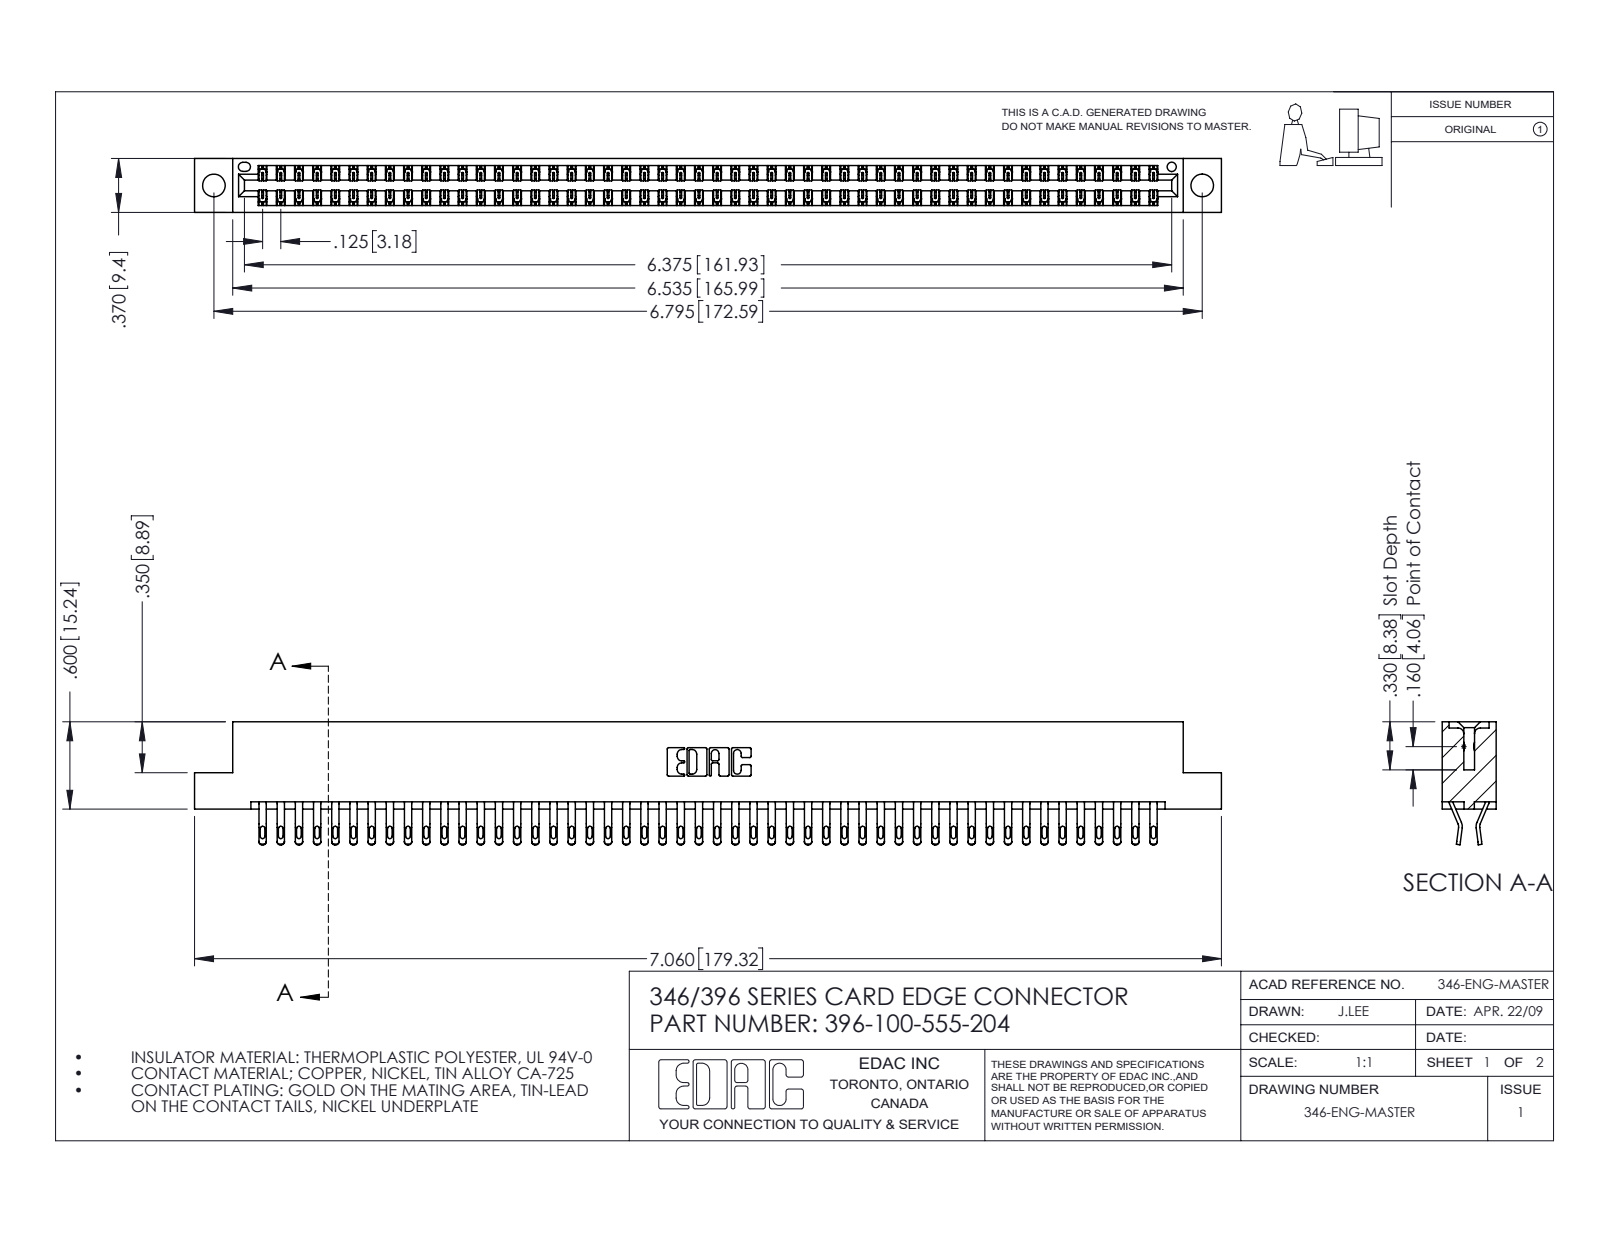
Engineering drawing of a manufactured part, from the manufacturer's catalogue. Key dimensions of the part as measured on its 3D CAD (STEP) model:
Part name (STEP PRODUCT): 396-100-555-204; 346 Part_Flush Mounting Lugs - 0.156 Dia-TH; 345-292-001_555 Tail
STEP written by: SolidWorks 2016 (CONFIG_CONTROL_DESIGN)
Units: inches
Bodies: 101 solids, 5922 faces (3376 planar, 2546 cylindrical, 0 other)
Overall size (bounding box): 7.06 × 0.845 × 0.37
Volume: 1.083 in³ · Surface area: 39.33 in²
Round holes (diameter × count): ⌀0.156 ×2, ⌀0.064 ×1
Partial cylindrical surfaces — rounded edges, fillets, slot ends (radius × count): R0.016 ×200, R0.02 ×200, R0.006 ×150, R0.01 ×22, R0.007 ×6, R0.031 ×6, R0.026 ×3, R0.01 ×2
Main face-to-face distances: 0.048, 0.322, 0.37, 0.25, 0.025, 0.072, 0.298, 0.275, 0.148, 0.222
Hole centre spacings: 0.246, 6.586, 6.795
